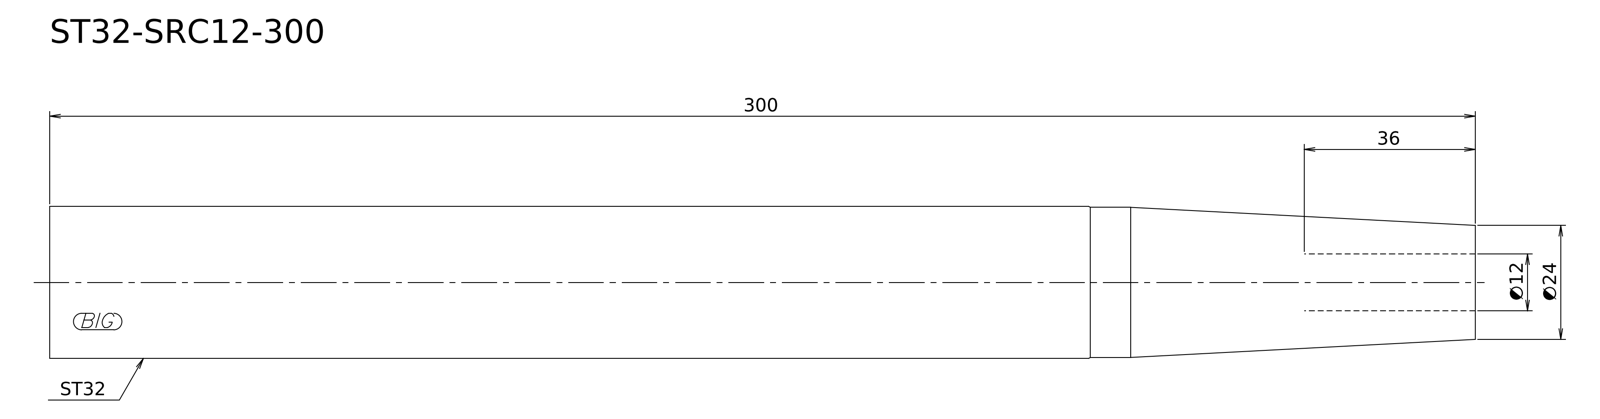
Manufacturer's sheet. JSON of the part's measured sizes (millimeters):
{"step_written_by": "Kubotek KeyCreator V8.5.1 (14335) (CONFIG_CONTROL_DESIGN)", "units": "millimeters", "bodies": {"solids": 1, "faces": 6, "planar": 2, "cylindrical": 2, "other": 2}, "overall_size": [300, 32, 32], "volume_mm3": 227072, "surface_area_mm2": 30462, "round_bosses_or_shafts": [[32, 1], [31.6, 1]], "face_to_face_distances": [300]}
